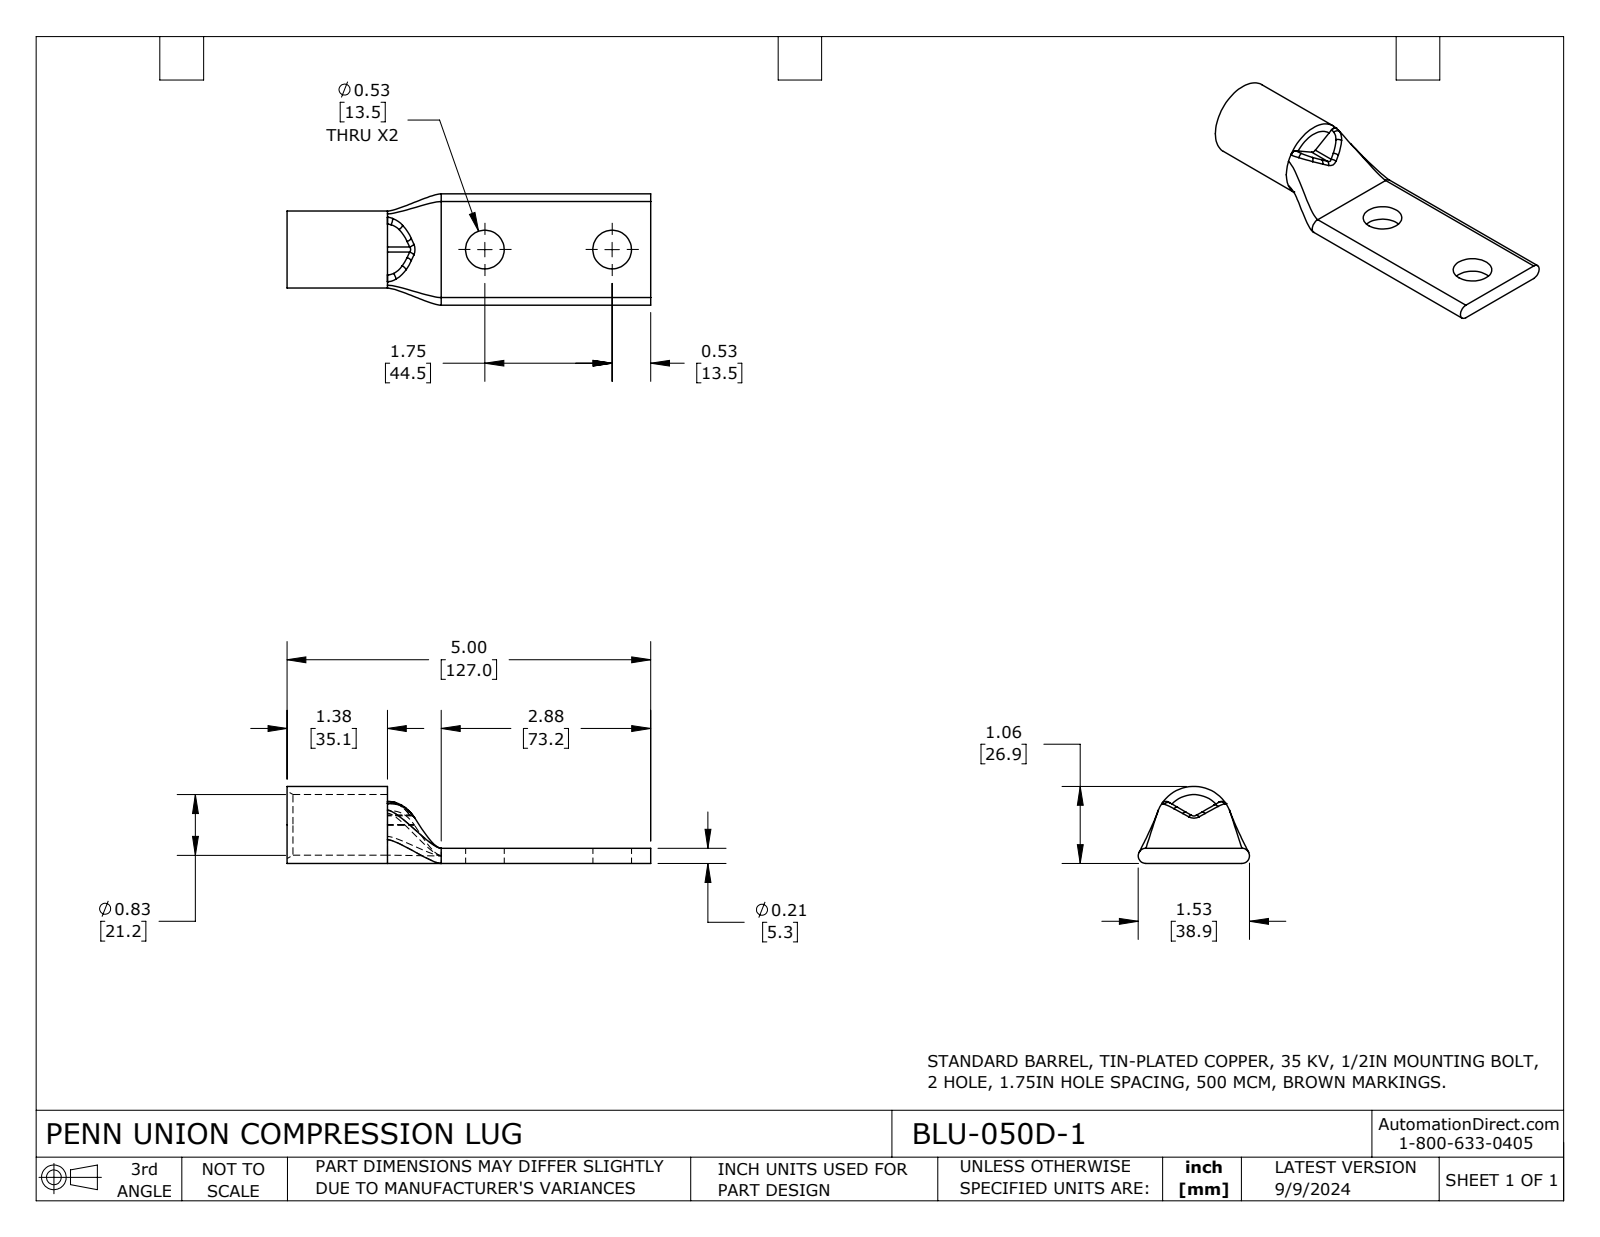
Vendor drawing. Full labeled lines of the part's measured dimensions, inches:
Part name (STEP PRODUCT): BLU-050D-1
STEP written by: SolidWorks 2023 (CONFIG_CONTROL_DESIGN)
Units: inches
Bodies: 1 solid, 45 faces (11 planar, 13 cylindrical, 21 other)
Overall size (bounding box): 5 × 1.53 × 1.06
Volume: 1.489 in³ · Surface area: 23.16 in²
Round holes (diameter × count): ⌀0.531 ×2, ⌀0.834 ×1
Round bosses / shafts (diameter × count): ⌀1.06 ×1
Partial cylindrical surfaces — rounded edges, fillets, slot ends (radius × count): R0.07 ×2, R0.105 ×2
Main face-to-face distances: 0.21, 5, 1.38, 3.62, 0.113, 2.12, 0.74, 2.88
Hole centre spacings: 1.75
